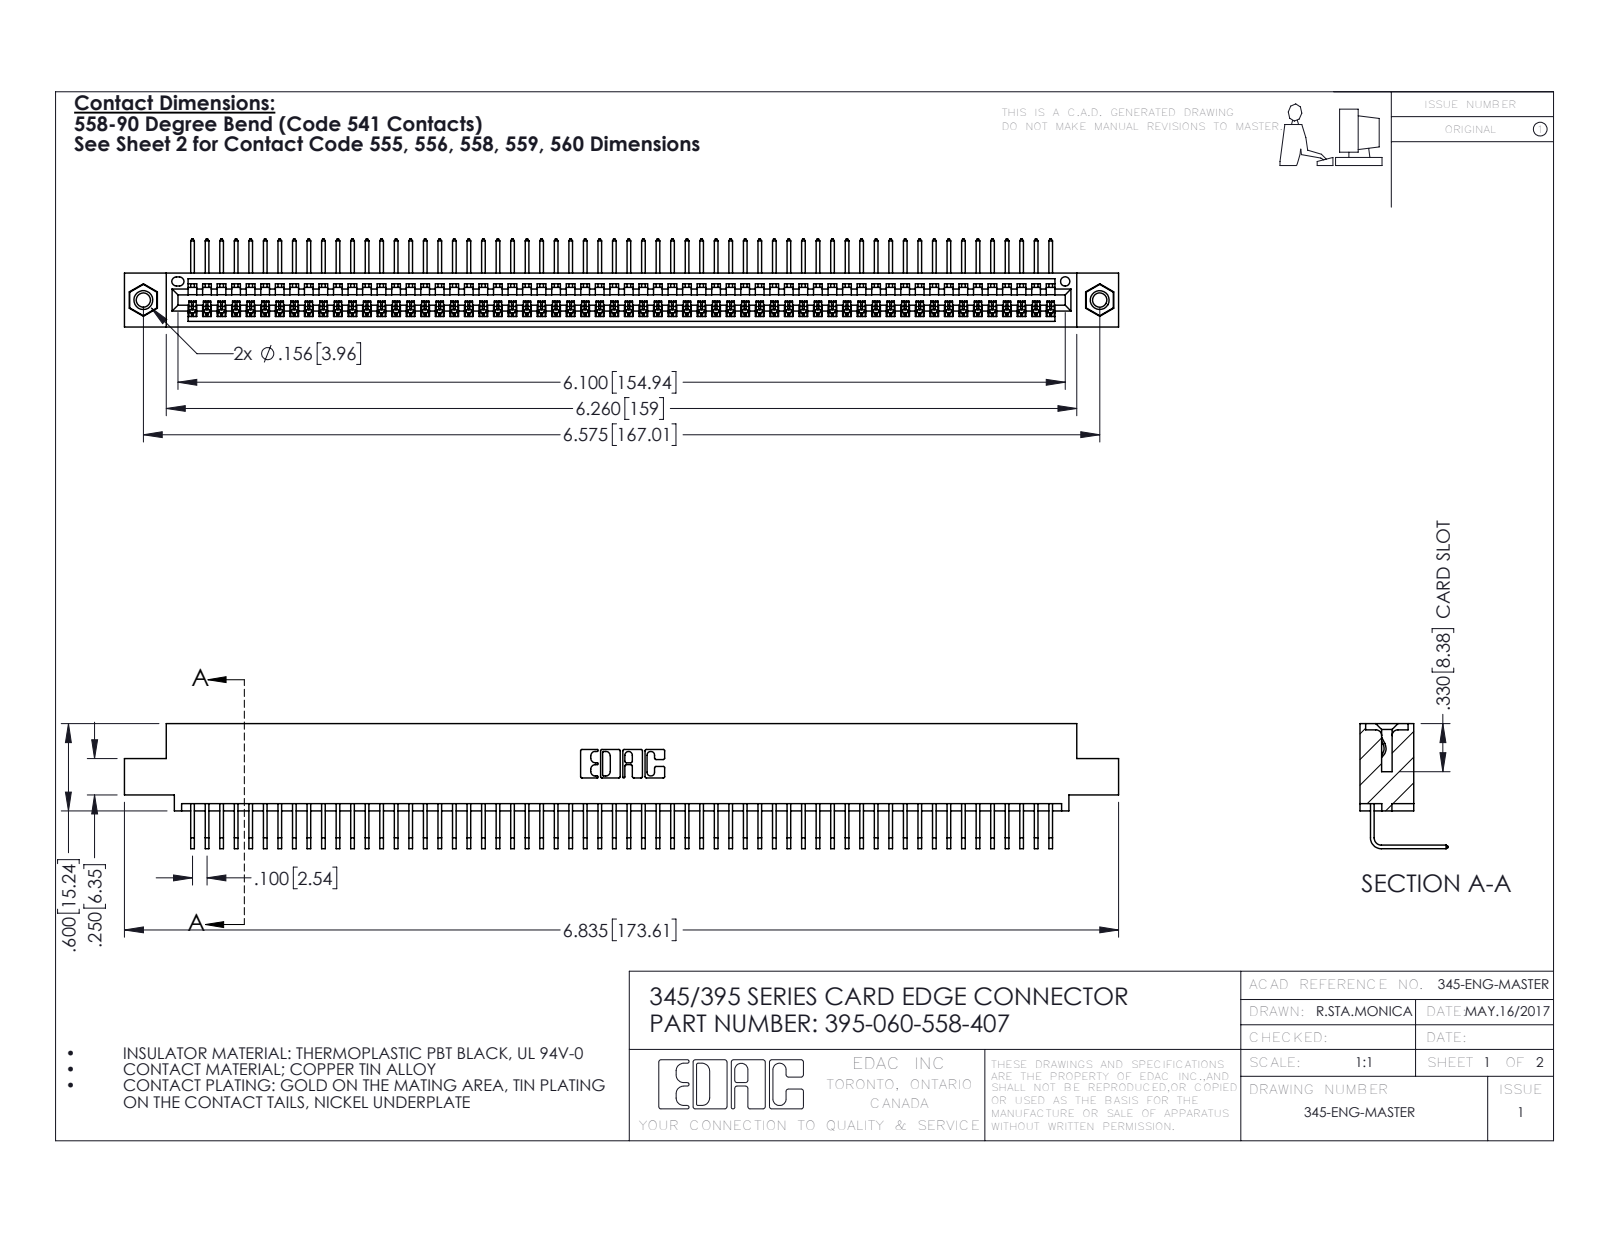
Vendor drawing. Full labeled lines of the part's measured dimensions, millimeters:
Part name (STEP PRODUCT): 395-060-558-407; 345-250-001_345-250-005-103; 345 Part_0.110 Offset - 0.156 Dia-TI; 345-292-001_558 Tail - 2
STEP written by: SolidWorks 2016 (CONFIG_CONTROL_DESIGN)
Units: millimetres
Bodies: 63 solids, 3790 faces (2636 planar, 1138 cylindrical, 16 other)
Overall size (bounding box): 173.6 × 21.8 × 15.4
Volume: 16 750 mm³ · Surface area: 23 790 mm²
Round holes (diameter × count): ⌀2.5 ×2, ⌀3.2 ×2, ⌀4 ×2, ⌀1.6 ×1
Round bosses / shafts (diameter × count): ⌀3.9 ×2
Partial cylindrical surfaces — rounded edges, fillets, slot ends (radius × count): R0.2 ×120, R0.3 ×22, R0.2 ×6, R0.8 ×6, R0.7 ×3, R0.8 ×2, R1 ×2, R0.4 ×1
Main face-to-face distances: 1.8, 7.6, 9.4, 5.1, 2.5, 6.9, 0.6, 5.7, 3.8, 1.8
Hole centre spacings: 6.9, 161, 167
